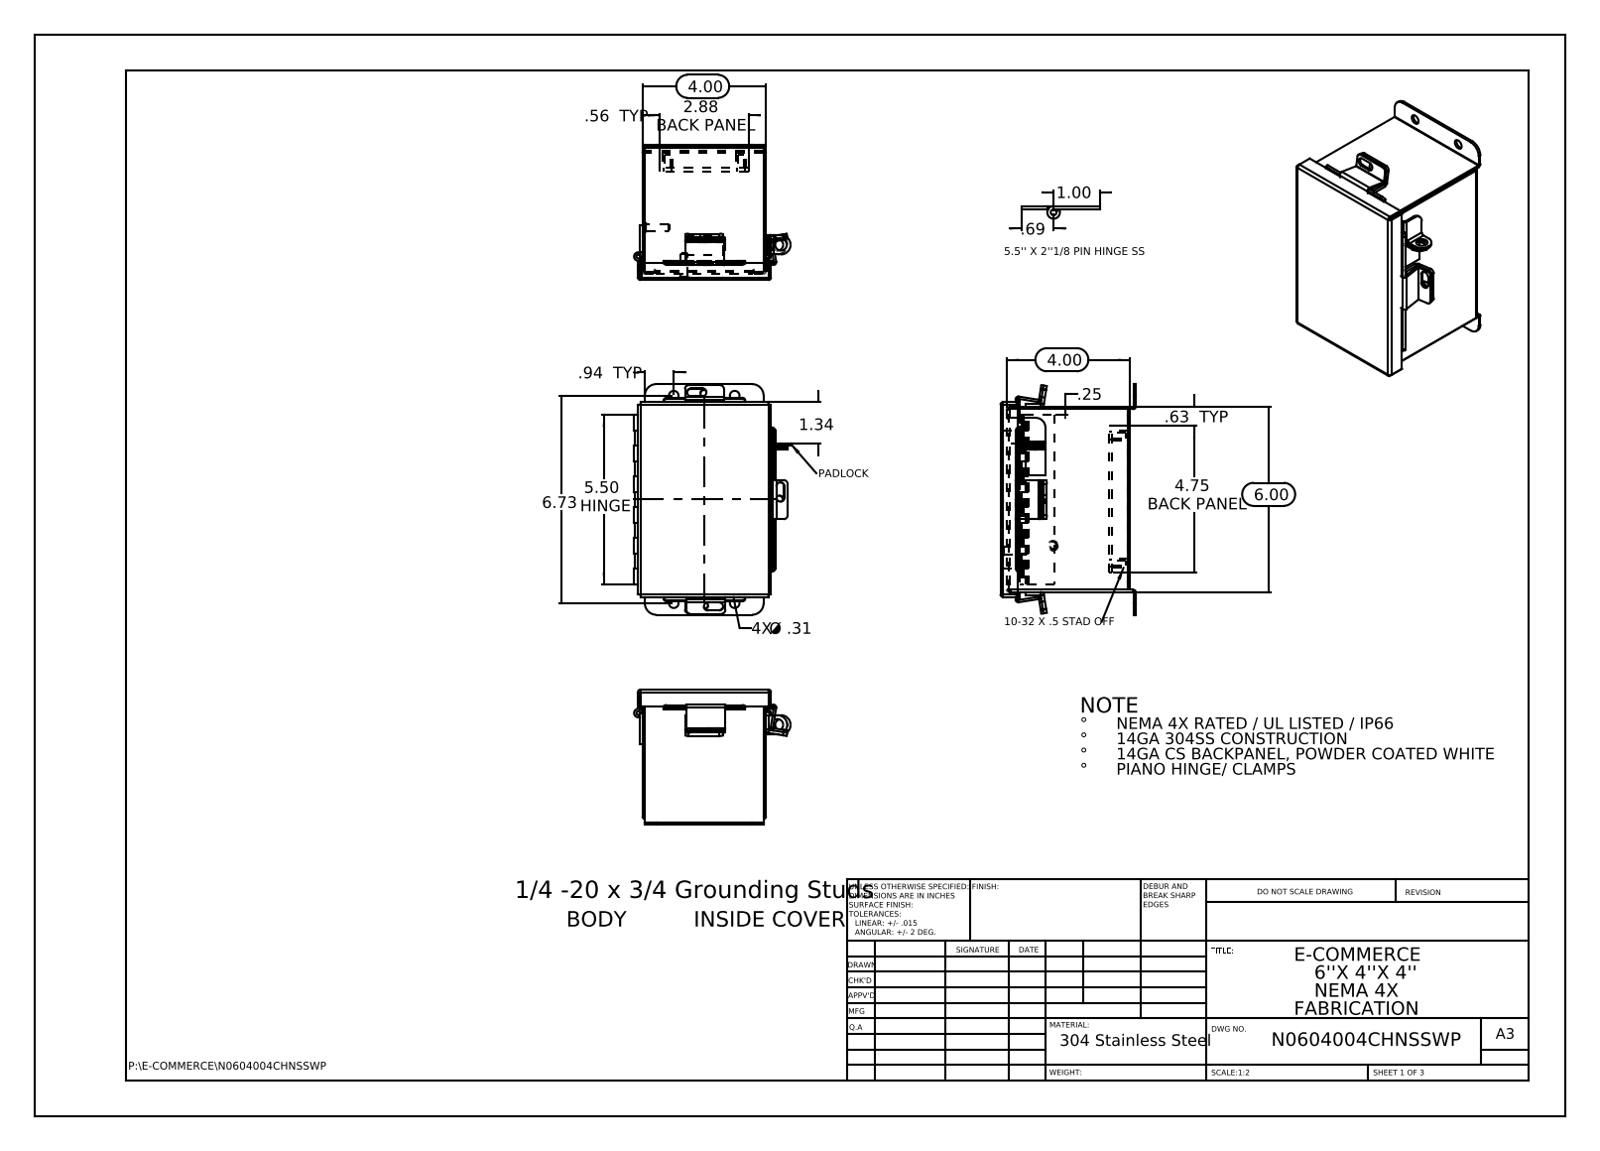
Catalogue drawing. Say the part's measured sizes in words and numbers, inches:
The part is named "N0604004CHNSSWP Hinge Cover Side JIC; N0604004CHNSSWP JIC Backpanel; N0604004CHNSSWP JIC Enclosure Template; N0604004CHNSSWP JIC Clamp Bracket (+8 more)". Its 3-D file was written by "SolidWorks 2013 (CONFIG_CONTROL_DESIGN)". It is 21 solids with 548 faces: 343 planar, 185 cylindrical and 20 other. Overall it measures 7.476 by 5.072 by 4.39 inches. Its volume is 14.49 cubic inches and its surface area 392.7 square inches. Round holes: 7 of diameter 0.25, 4 of diameter 0.187, 4 of diameter 0.312, 1 of diameter 0.125, 1 of diameter 0.125, 1 of diameter 0.373, 1 of diameter 0.375. Round bosses or shafts: 4 of diameter 0.313, 2 of diameter 0.315, 2 of diameter 0.236, 1 of diameter 0.273, 1 of diameter 0.25. Partial cylindrical surfaces (rounded edges, fillets, slot ends): 13 of radius 0.013, 12 of radius 0.009, 12 of radius 0.088, 10 of radius 0.125, 6 of radius 0.083, 6 of radius 0.1, 6 of radius 0.133, 4 of radius 0.375. The main face-to-face distances are 0.075, 3.925, 4.128, 5.925, 4, 3.85, 4.053, 4.203, 5.85, 6. The hole center spacings are 1.315, 2.534, 5.43, 5.846, 1.976, 2.375, 4.126, 4.761.
